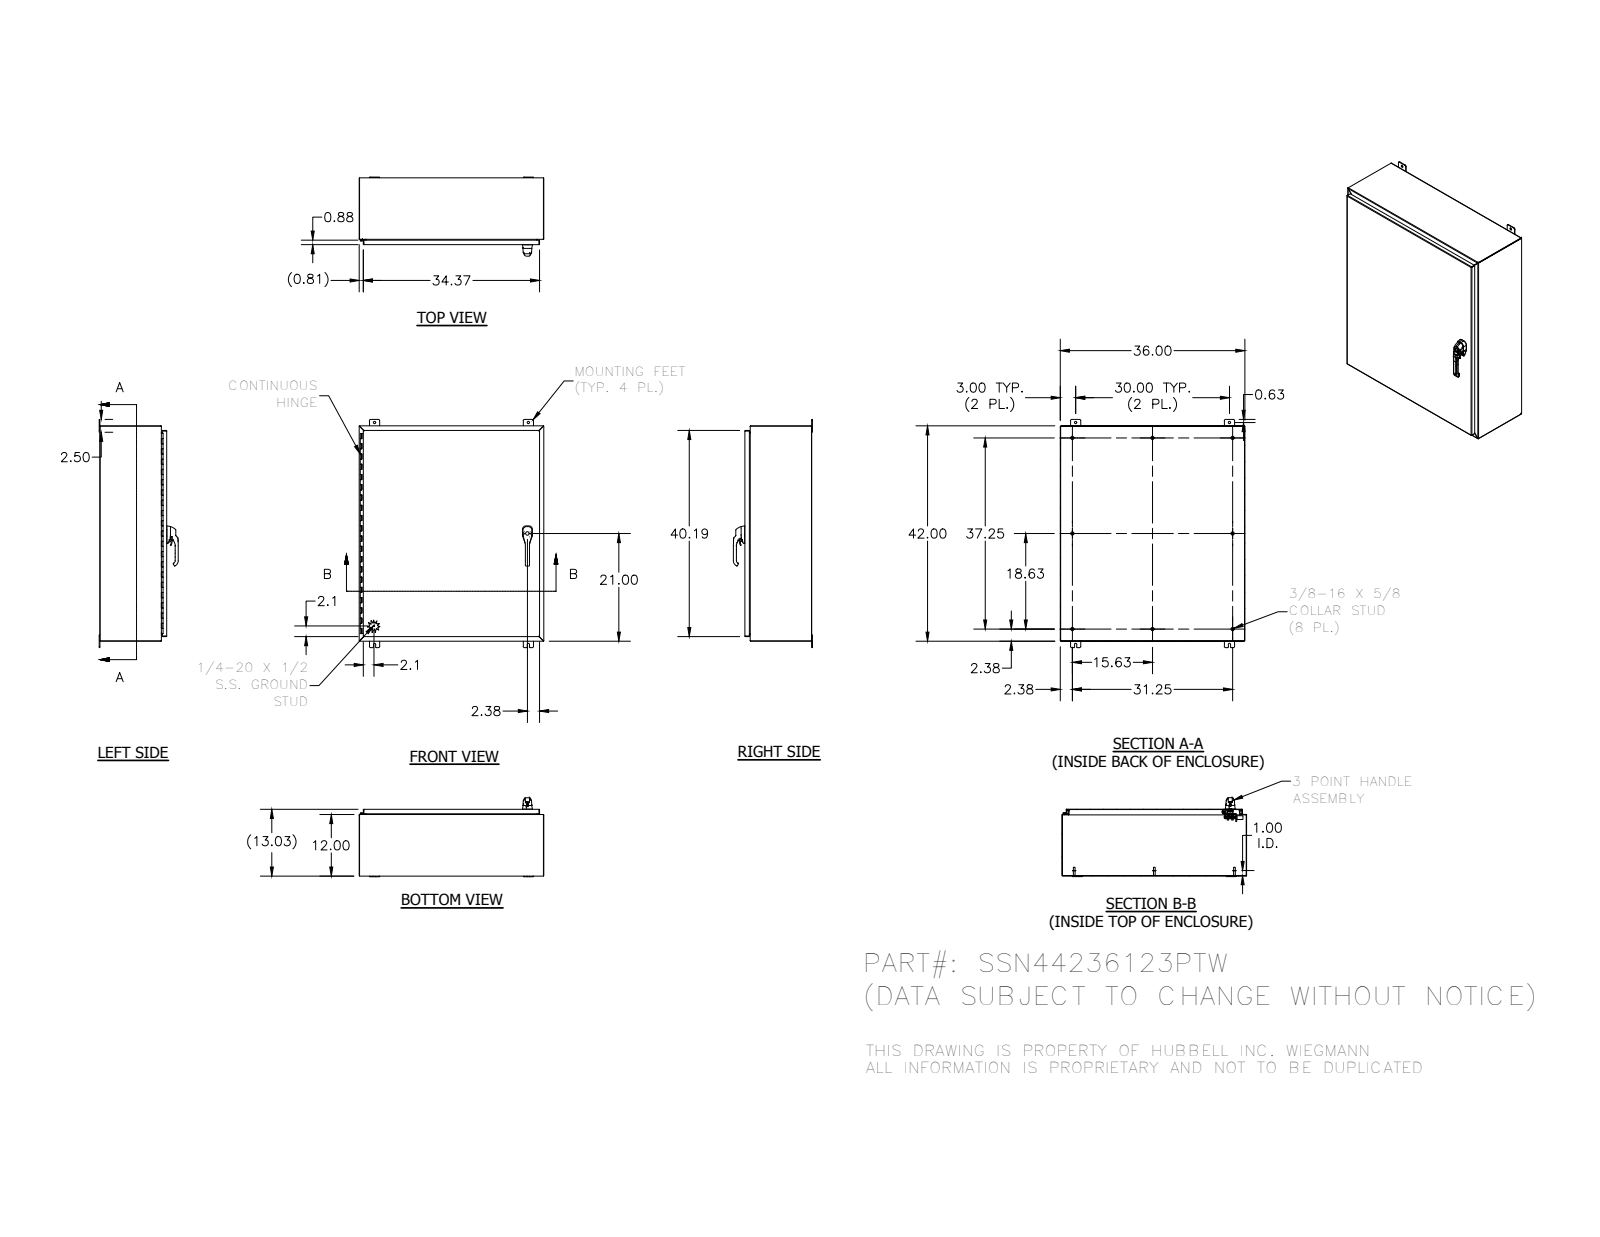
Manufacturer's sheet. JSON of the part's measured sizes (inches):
{"part_name": "1000-277-01; SSN44236123PTWBTB; PLASTIC-ROLLER-CAM_AF1; LOCK-NUT_AF0 (+8 more)", "step_written_by": "SolidWorks 2014 (AUTOMOTIVE_DESIGN)", "units": "inches", "bodies": {"solids": 62, "faces": 3279, "planar": 1156, "cylindrical": 1338, "other": 785}, "overall_size": [44.5, 36, 15.408], "volume_in3": 424.2, "surface_area_in2": 11170, "round_holes": [[0.262, 8], [0.187, 4], [0.438, 4], [0.213, 3], [0.281, 3], [0.241, 2], [0.25, 2], [0.252, 2], [0.315, 2], [0.4, 2], [0.402, 2], [0.413, 2]], "round_bosses_or_shafts": [[0.625, 8], [0.33, 8], [0.236, 3], [1, 2], [0.563, 2], [0.533, 2], [0.531, 2], [0.5, 2]], "partial_cylinders_radius": [[0.02, 171], [0.012, 113], [0.125, 26], [0.031, 22], [0.019, 21], [0.25, 20], [0.105, 18], [0.05, 15]], "face_to_face_distances": [0.074, 12.959, 12.885, 13.033, 35.926, 41.926, 35.852, 36, 41.852, 42], "hole_center_spacings": [0.38, 0.492, 0.76, 0.886, 32.428, 0.234, 0.258, 0.38]}
